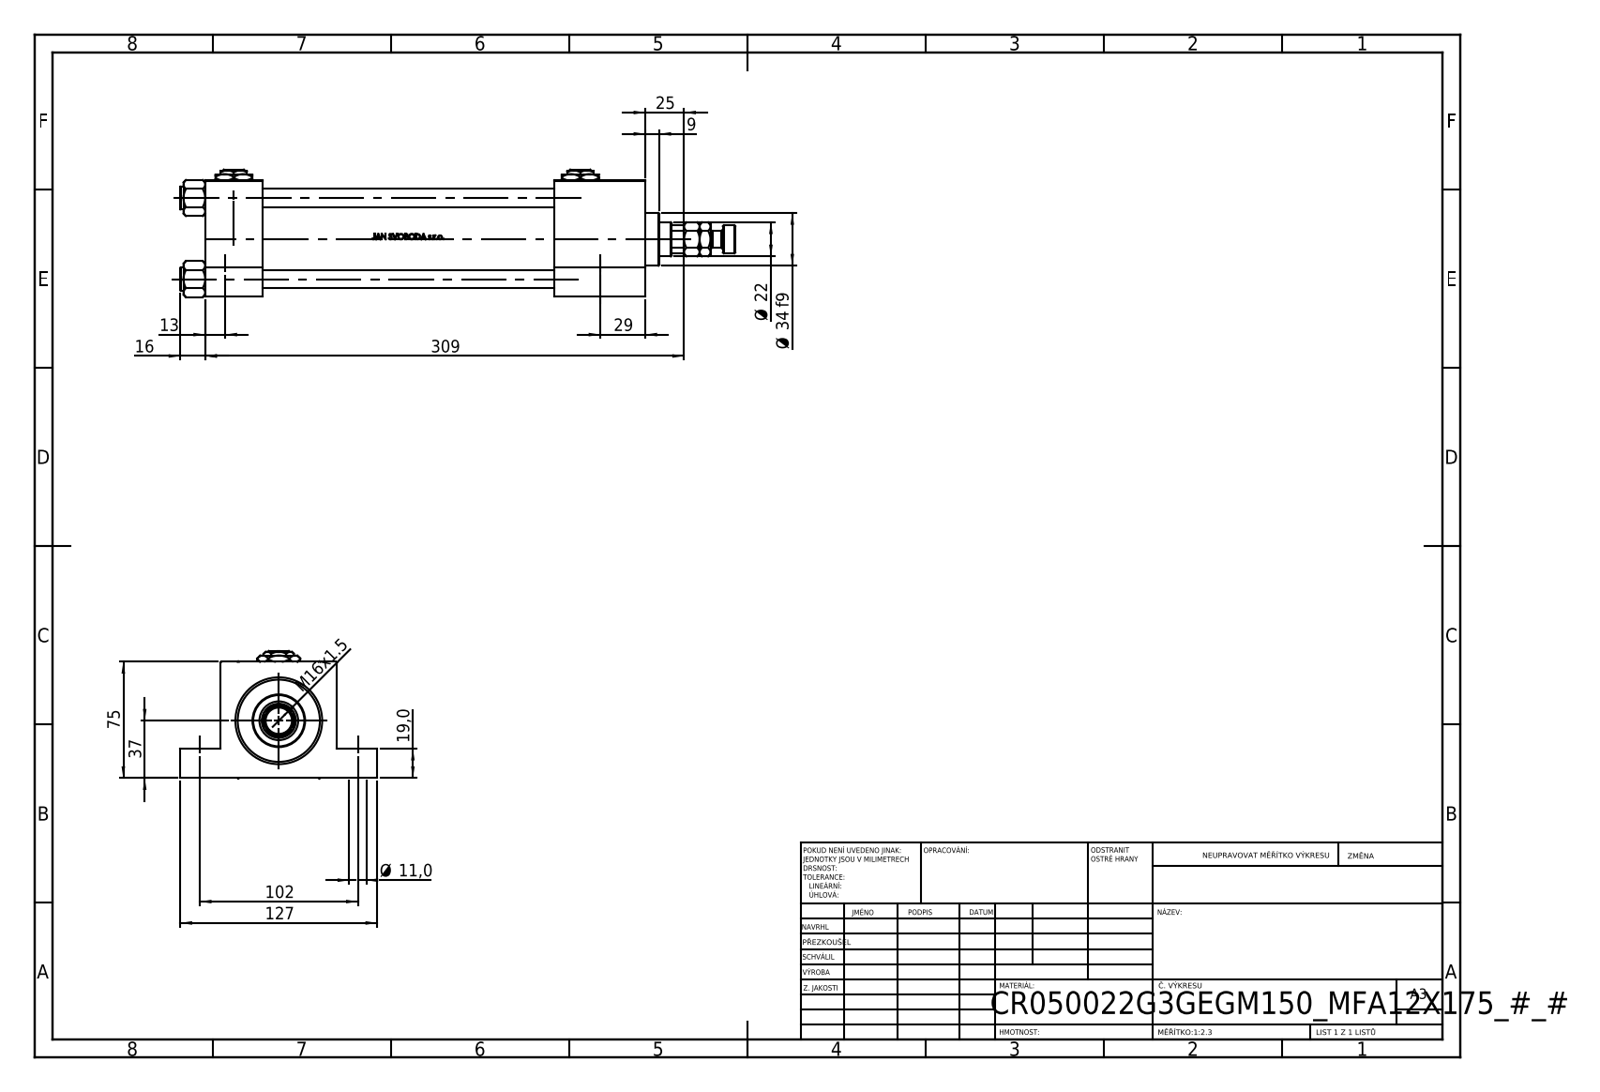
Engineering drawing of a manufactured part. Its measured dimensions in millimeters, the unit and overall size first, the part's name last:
Units: millimetres
Overall size (bounding box): 358 × 127 × 82.27
Round holes (diameter × count): ⌀11 ×4, ⌀12 ×4, ⌀7 ×2, ⌀20.96 ×2, ⌀30 ×2, ⌀10.5 ×1, ⌀22 ×1, ⌀25 ×1, ⌀41 ×1, ⌀50 ×1, ⌀53 ×1
Round bosses / shafts (diameter × count): ⌀15 ×4, ⌀56 ×1, ⌀34 ×1, ⌀18 ×1, ⌀11 ×1
Partial cylindrical surfaces — rounded edges, fillets, slot ends (radius × count): R10.5 ×1
Main face-to-face distances: 75, 37, 284, 247, 19, 56, 225, 188, 59, 101
Hole centre spacings: 52.3, 36.63, 37.34, 51.3, 52.63, 73.96, 102, 234.61
Volume: 942 456 mm³ · Surface area: 236 869 mm²
Bodies: 14 solids, 1224 faces (492 planar, 128 cylindrical, 604 other)
Part name (STEP PRODUCT): MFA; V215CR_VCP_G; NUT_M5_G; Zatka_pro_OIL_PORT (+3 more)
STEP written by: SolidWorks 2019 (CONFIG_CONTROL_DESIGN)
